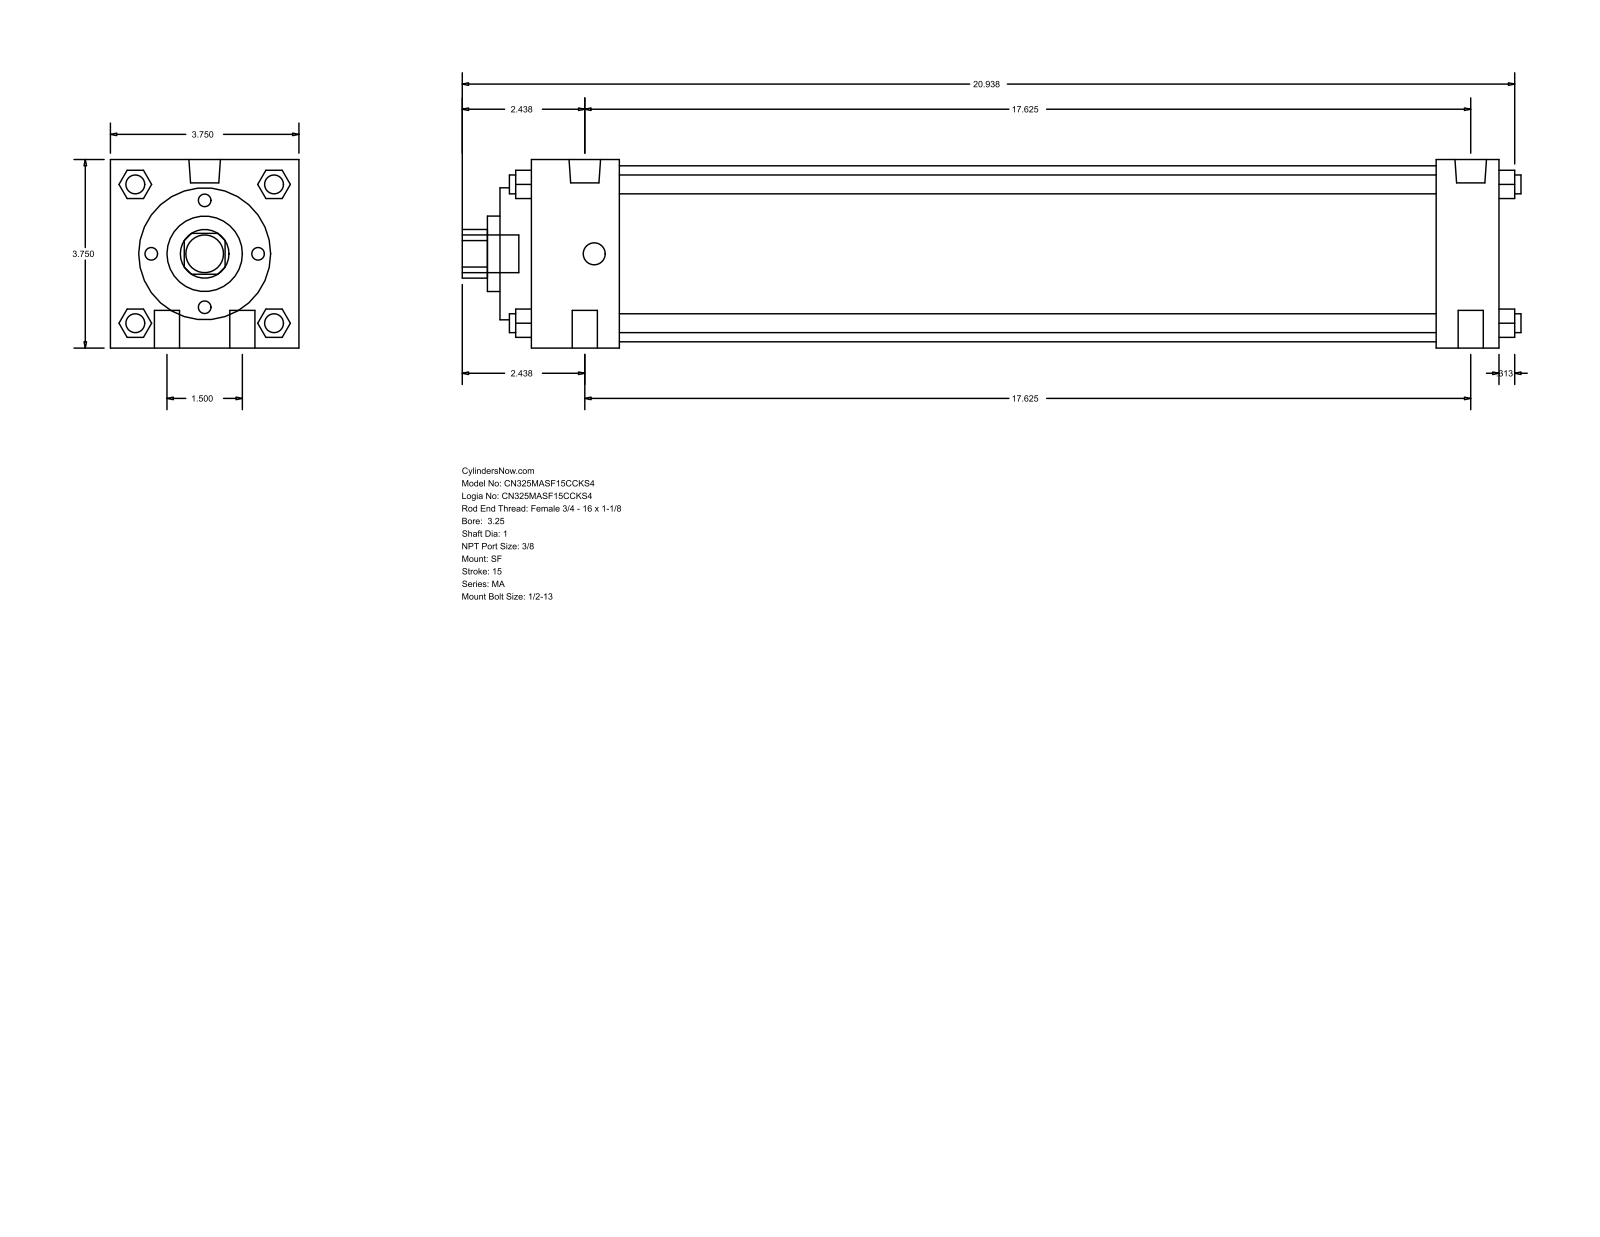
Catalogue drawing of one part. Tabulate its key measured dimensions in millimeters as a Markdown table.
| quantity | value |
| --- | --- |
| part name | MA_SF__0325_1 |
| STEP written by | GSSL Pune (CONFIG_CONTROL_DESIGN) |
| units | millimeters |
| bodies | 0 solids, 126 faces (95 planar, 31 cylindrical, 0 other) |
| overall size | 534.99 × 95.25 × 95.25 |
| round holes (diameter × count) | 25.4 × 1, 38.1 × 1, 66.67 × 1, 88.9 × 1 |
| round bosses / shafts (diameter × count) | 12.7 × 4, 9.53 × 4, 15.93 × 2, 11.11 × 2, 19.05 × 1 |
| partial cylindrical surfaces (radius × count) | 12.29 × 1 |
| main face-to-face distances | 95.24, 488.96, 15.87, 457.2, 31.76, 44.46, 412.74, 444.5, 60.33, 473.07 |
